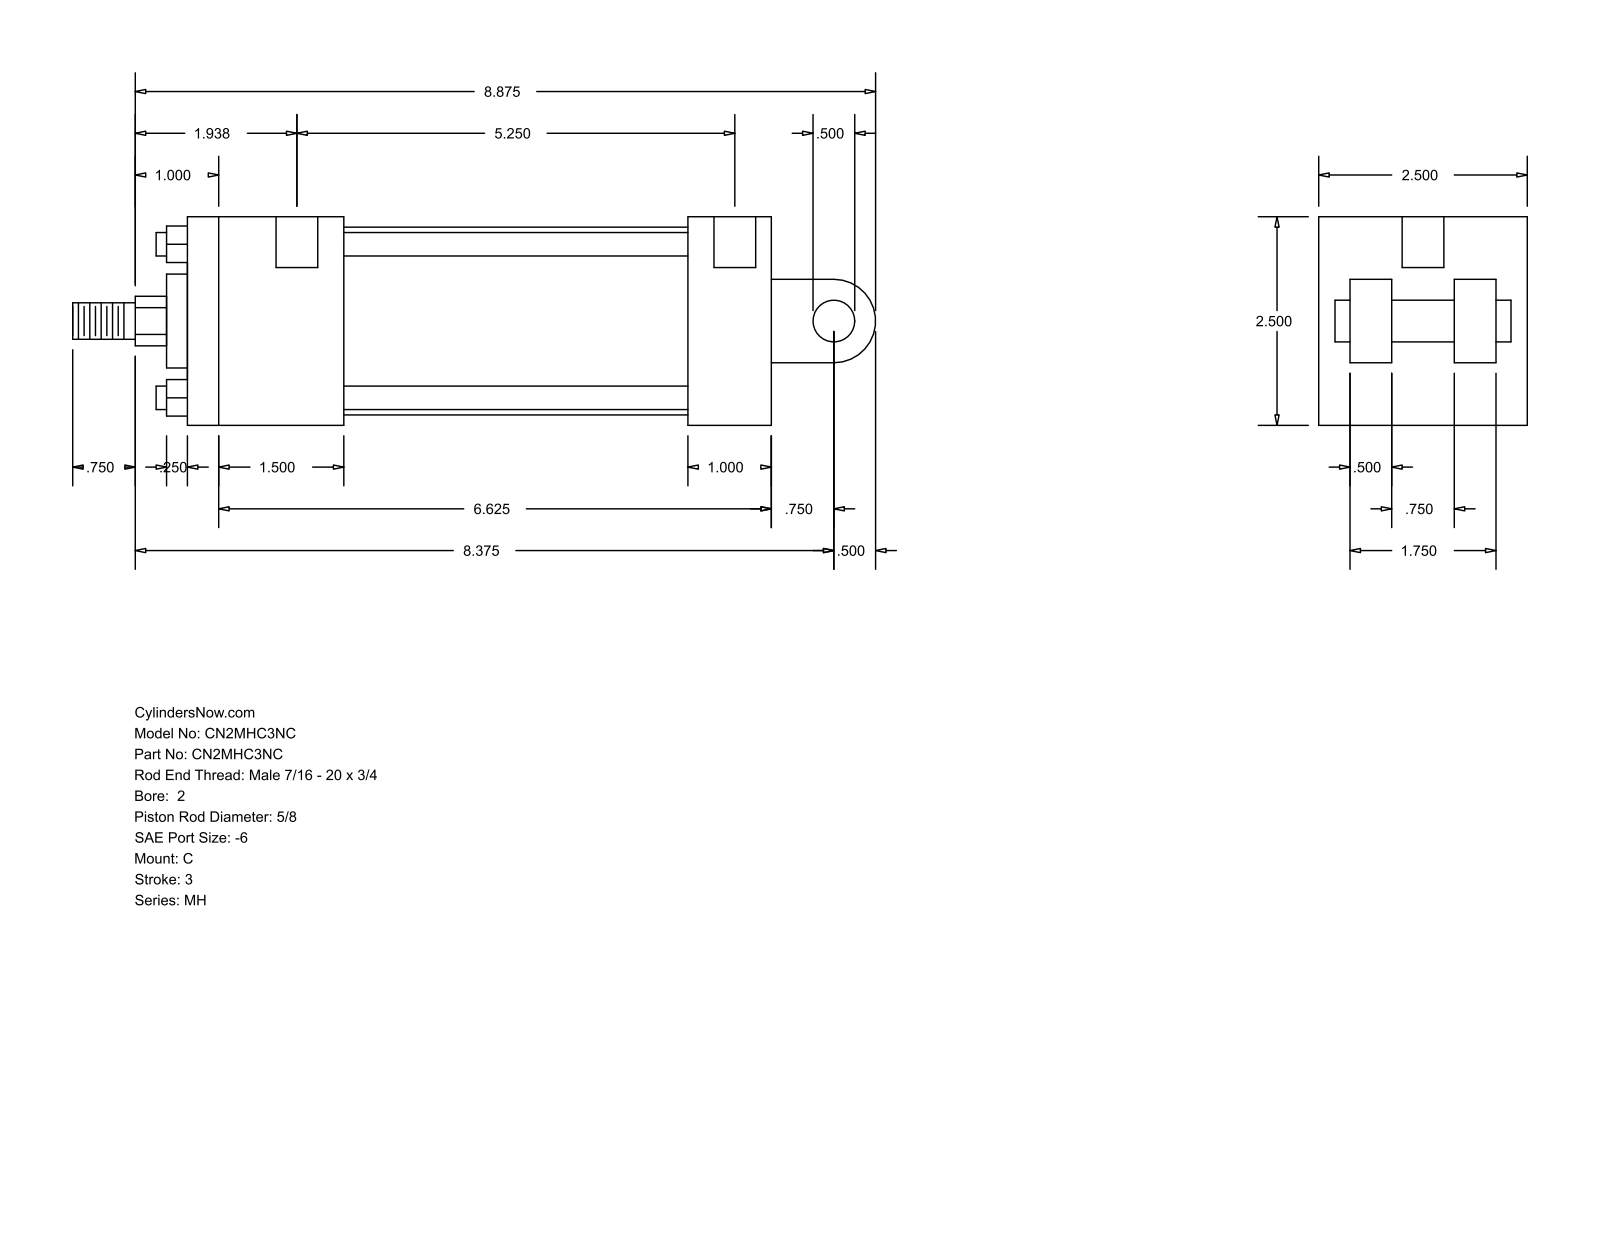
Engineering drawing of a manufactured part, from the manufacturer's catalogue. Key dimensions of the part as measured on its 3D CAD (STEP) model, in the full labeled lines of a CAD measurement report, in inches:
Part name (STEP PRODUCT): MH_C__0200_0.625
STEP written by: GSSL Pune (CONFIG_CONTROL_DESIGN)
Units: inches
Bodies: 0 solids, 99 faces (70 planar, 29 cylindrical, 0 other)
Overall size (bounding box): 9.625 × 2.5 × 2.5
Round holes (diameter × count): ⌀0.219 ×4, ⌀0.5 ×2
Round bosses / shafts (diameter × count): ⌀0.281 ×4, ⌀2.25 ×1, ⌀1.125 ×1, ⌀0.625 ×1, ⌀0.5 ×1, ⌀0.437 ×1
Partial cylindrical surfaces — rounded edges, fillets, slot ends (radius × count): R0.297 ×1, R0.5 ×1
Main face-to-face distances: 2.5, 7, 1, 0.5, 1.875, 6, 4.125, 5.125, 0.75, 0.375
Hole centre spacings: 5.563, 0.125, 0.187, 5.25, 5.375, 5.437
